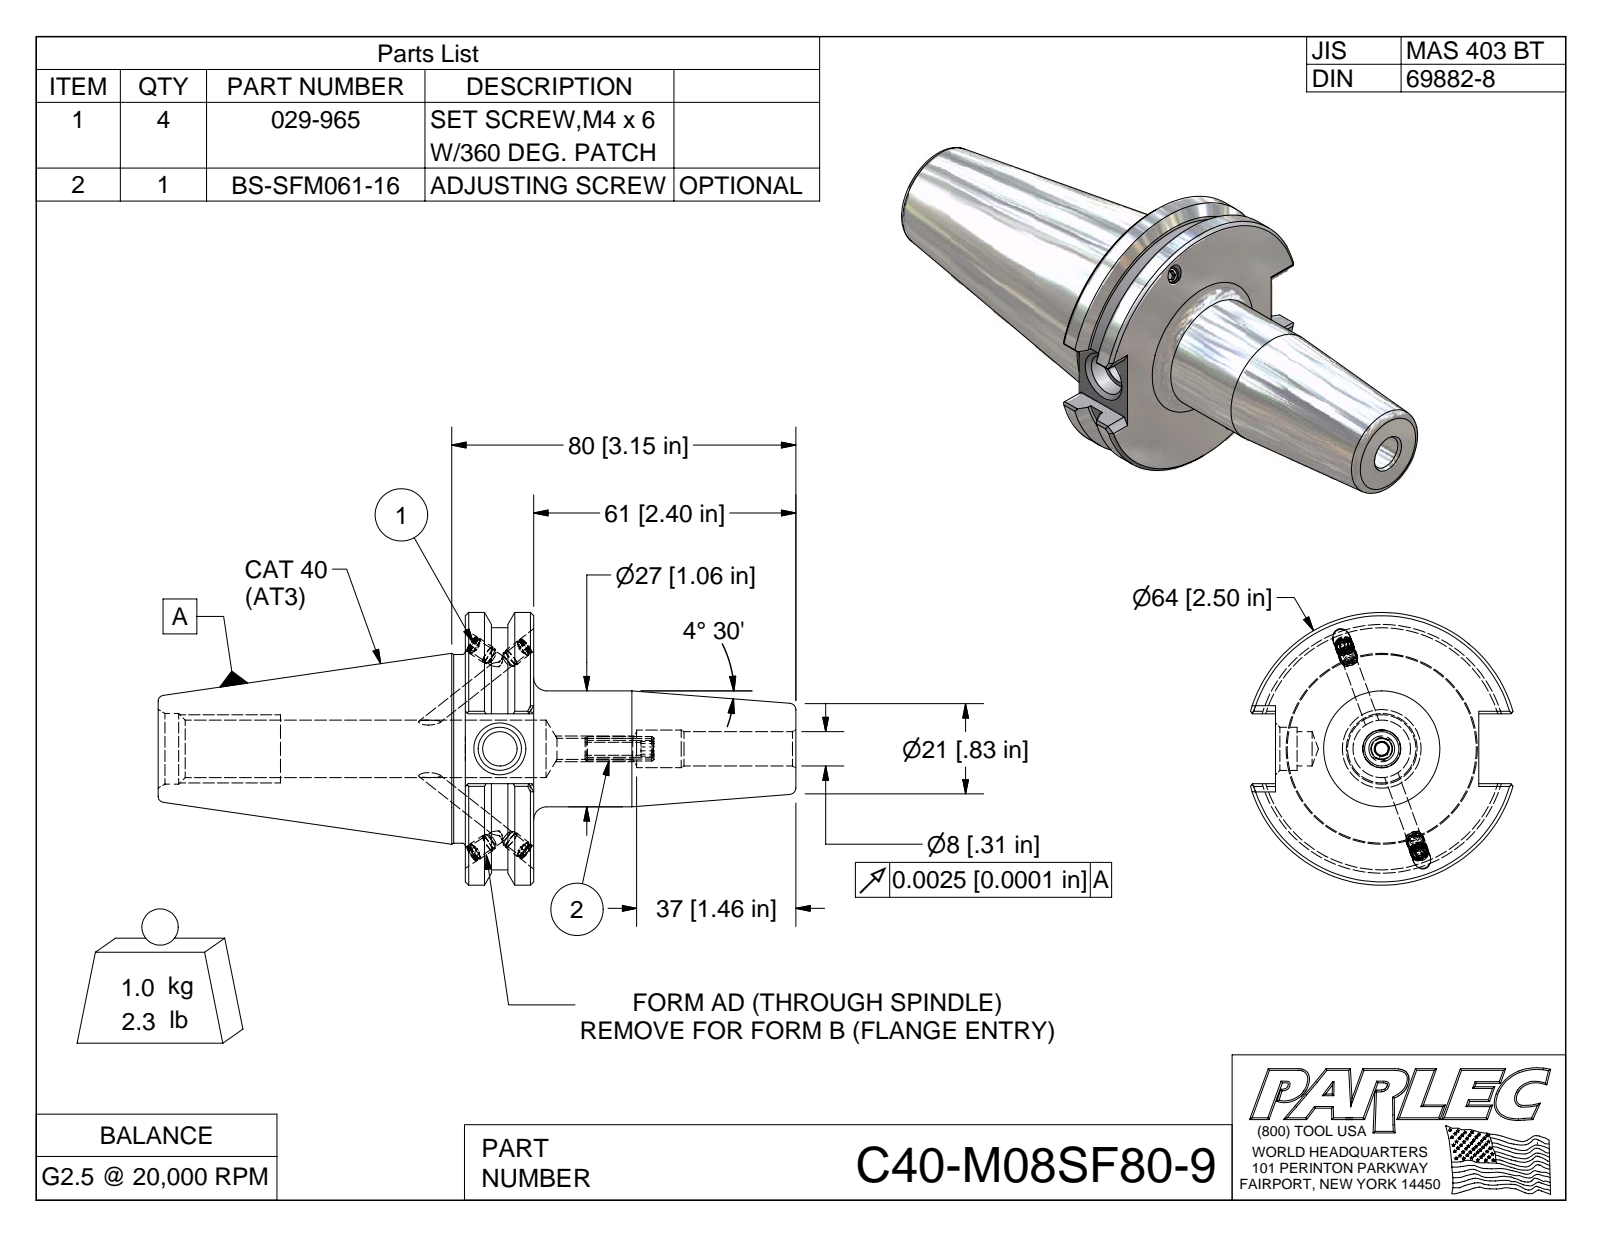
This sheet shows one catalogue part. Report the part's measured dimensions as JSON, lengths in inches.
{"part_name": "C40-M08SF80-9; C40BC-M08SF80-9-1; 029-965; BS-SFM061-16", "step_written_by": "Autodesk Inventor 2009 (AUTOMOTIVE_DESIGN)", "units": "inches", "bodies": {"solids": 6, "faces": 177, "planar": 87, "cylindrical": 32, "other": 58}, "overall_size": [5.837, 2.5, 2.403], "volume_in3": 7.8, "surface_area_in2": 43.33, "round_holes": [[0.13, 4], [0.161, 4], [0.314, 1], [0.344, 1]], "round_bosses_or_shafts": [[0.165, 4], [0.157, 4], [2.5, 1], [2.219, 1], [1.73, 1], [1.063, 1]], "partial_cylinders_radius": [[0.118, 1]], "face_to_face_distances": [0.625, 3.025, 2.4, 0.64, 1.86, 2.812, 3.437, 5.837, 3.201, 0.389]}
